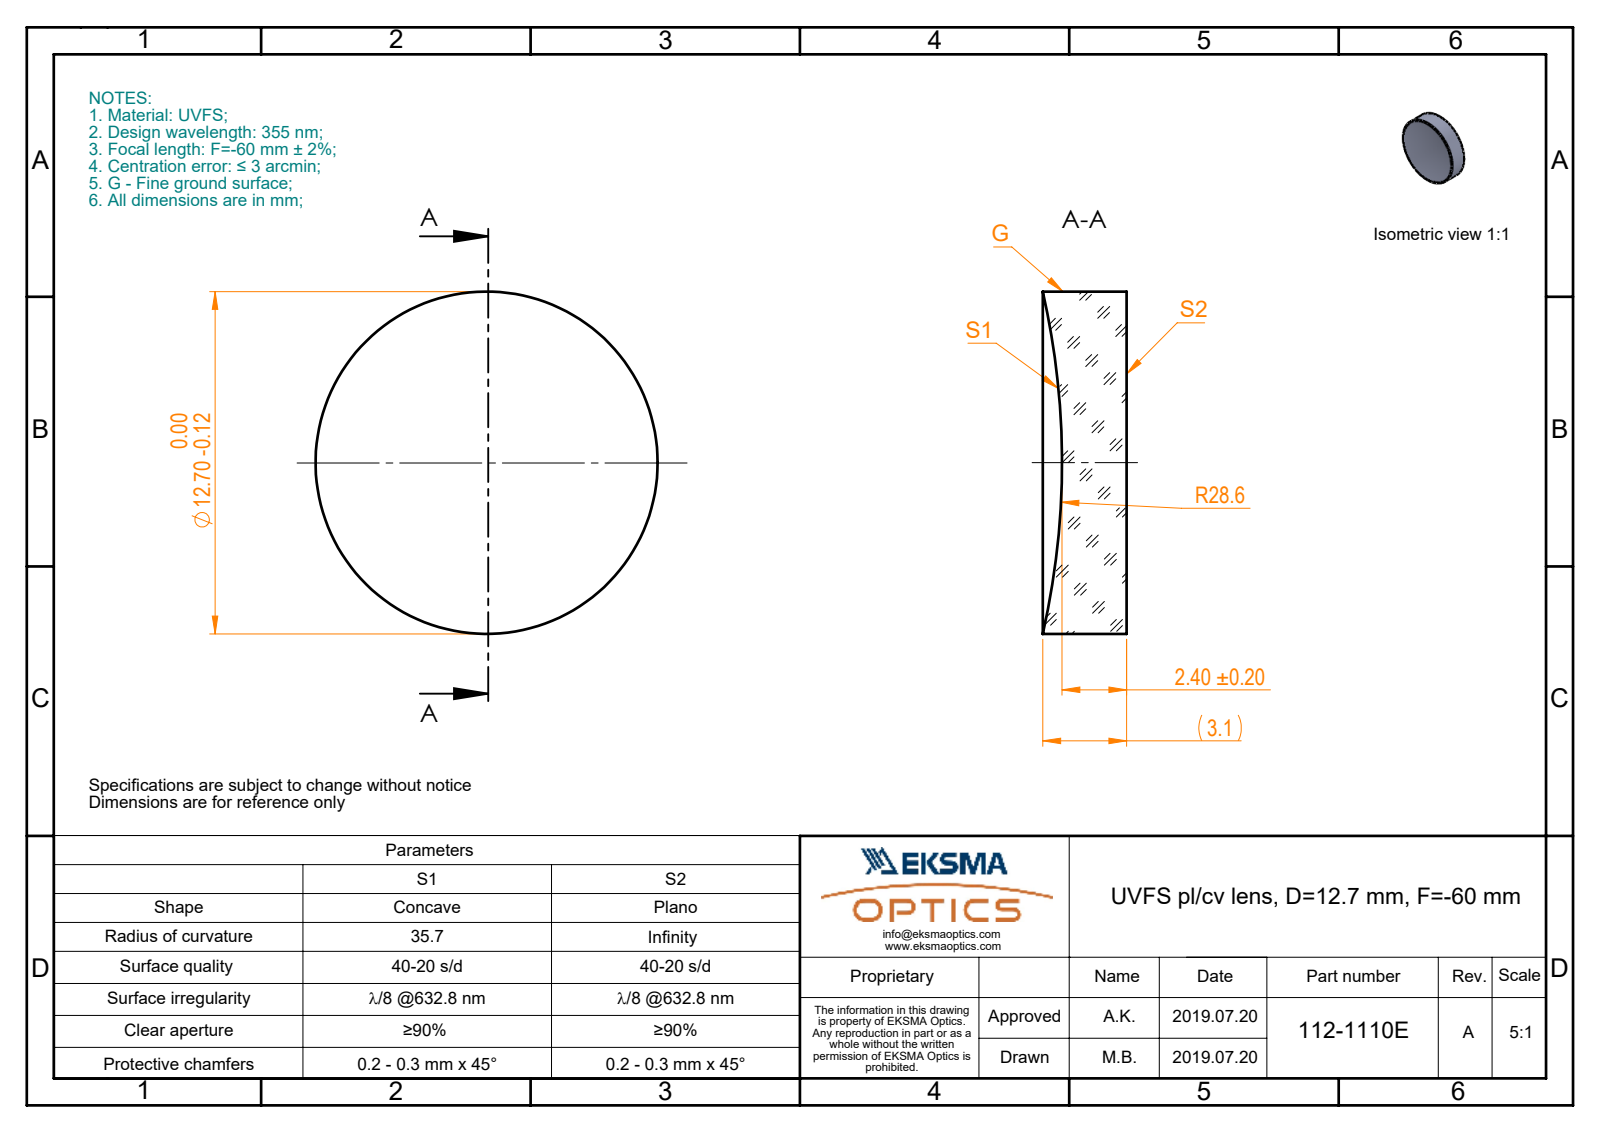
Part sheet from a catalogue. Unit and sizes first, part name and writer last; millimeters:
Units: millimetres
Overall size (bounding box): 12.7 × 12.7 × 3.12
Round bosses / shafts (diameter × count): ⌀12.7 ×1
Volume: 349 mm³ · Surface area: 379 mm²
Bodies: 1 solid, 5 faces (1 planar, 2 cylindrical, 2 other)
Part name (STEP PRODUCT): 112-1110E UVFS pl-cv 12.7 F-60
STEP written by: SolidWorks 2017 (CONFIG_CONTROL_DESIGN)
